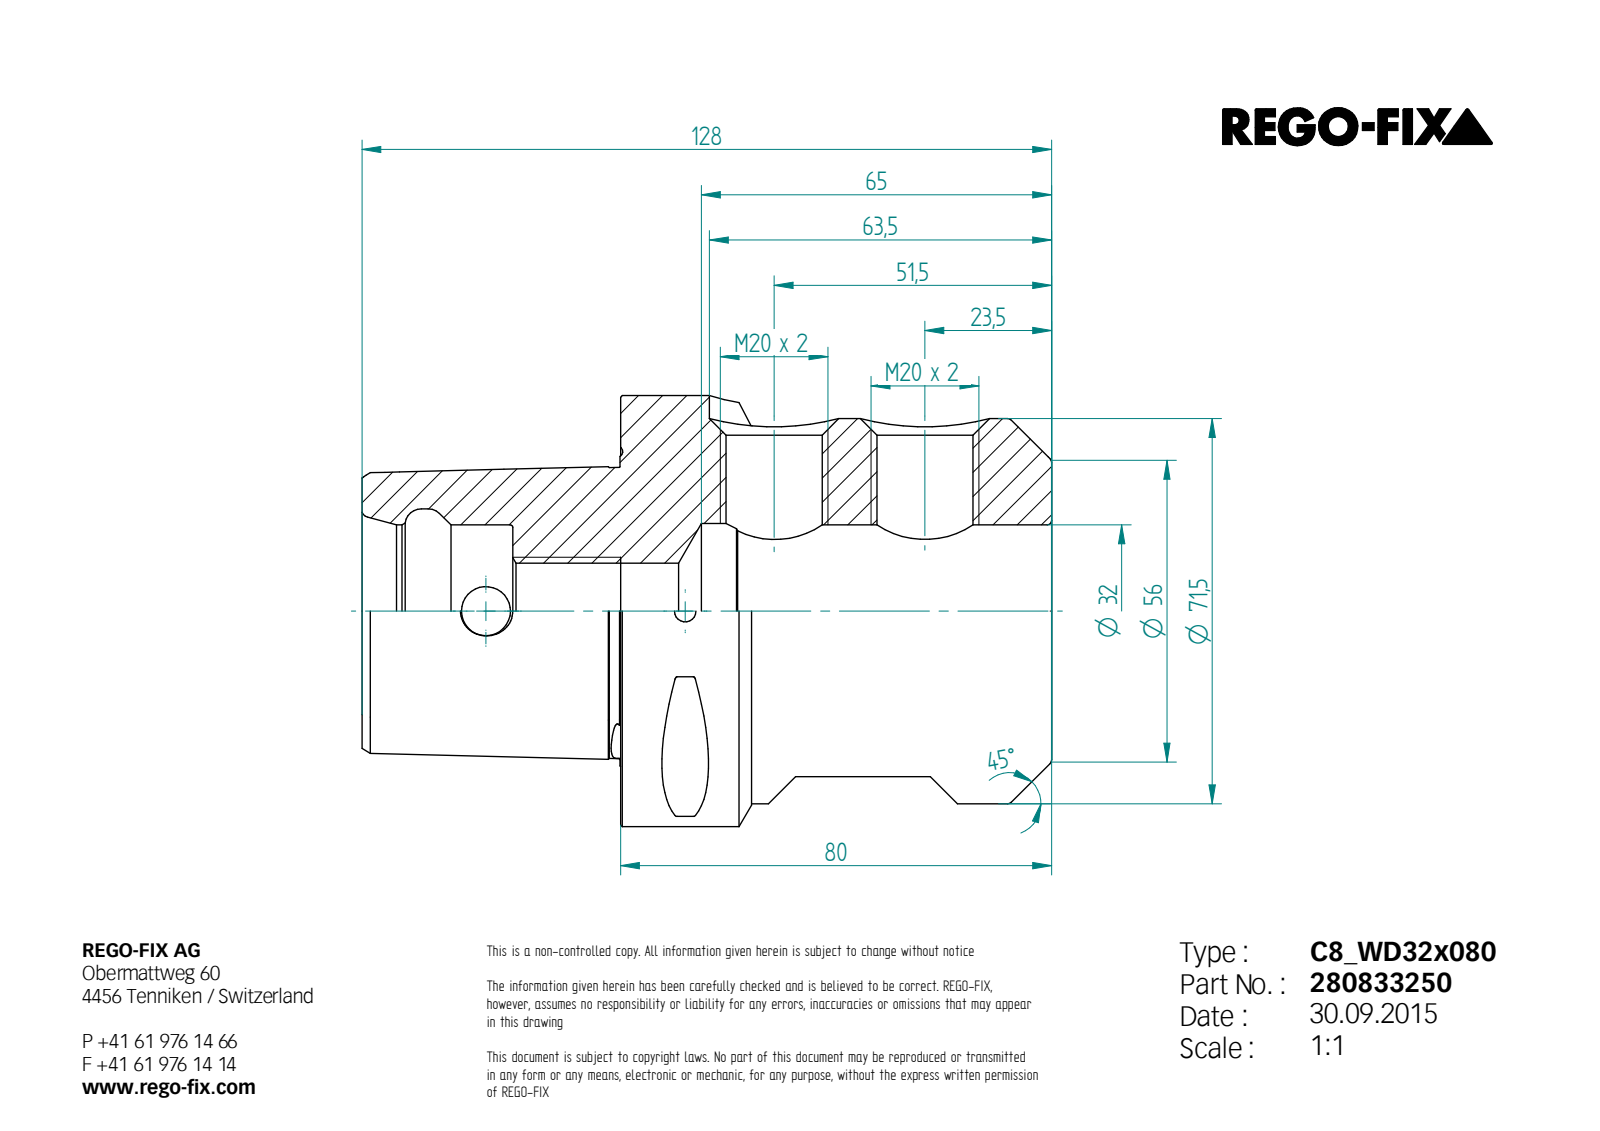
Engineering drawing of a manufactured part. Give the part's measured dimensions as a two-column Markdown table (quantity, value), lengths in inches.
| quantity | value |
| --- | --- |
| STEP written by | Unknown (AUTOMOTIVE_DESIGN) |
| units | inches |
| bodies | 1 solid, 106 faces (23 planar, 23 cylindrical, 60 other) |
| overall size | 5.039 × 3.15 × 3.15 |
| volume | 20.73 in³ |
| surface area | 74.27 in² |
| round holes (diameter × count) | 0.702 × 3, 0.157 × 1, 0.358 × 1, 1.26 × 1, 1.28 × 1, 1.496 × 1 |
| round bosses / shafts (diameter × count) | 3.15 × 1, 2.815 × 1 |
| partial cylindrical surfaces (radius × count) | 0.02 × 8, 0.472 × 1 |
| main face-to-face distances | 3.15, 1.89, 5.039, 1.281, 1.102, 0.787, 3.937, 1.886, 0.783, 3.154 |
| hole center spacings | 1.102, 1.457 |
